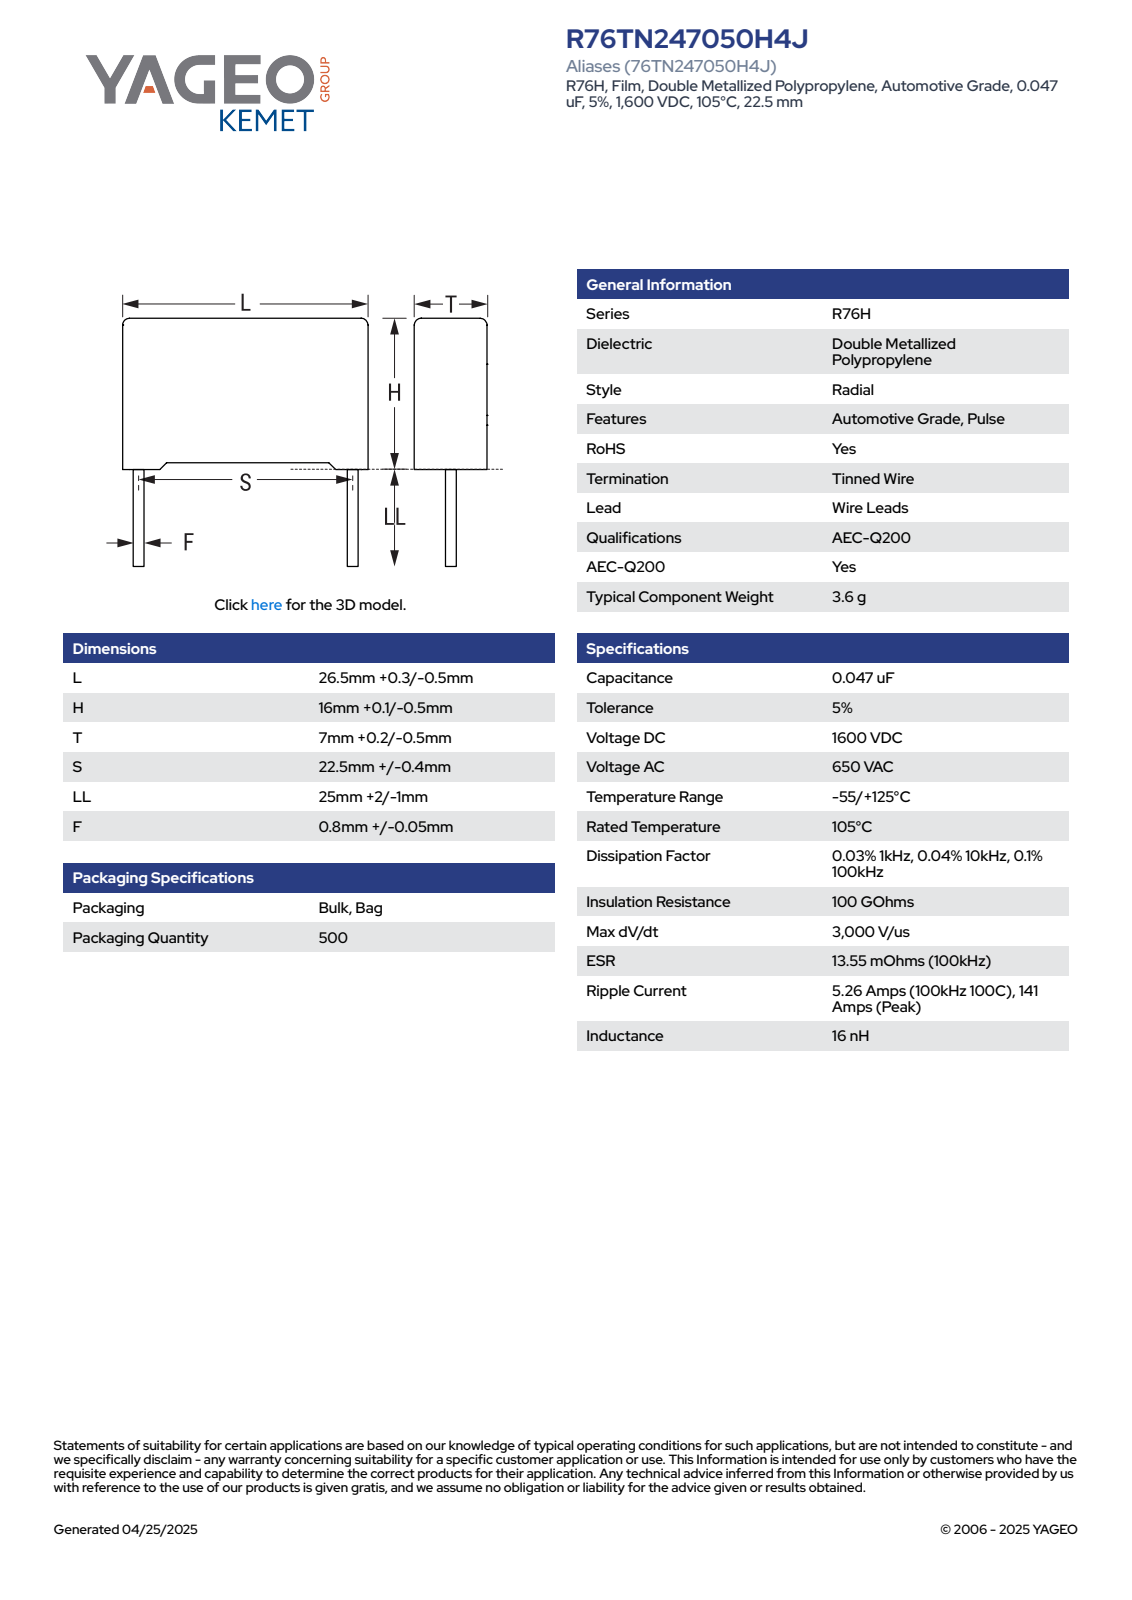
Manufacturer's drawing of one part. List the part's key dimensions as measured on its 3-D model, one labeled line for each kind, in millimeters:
Part name (STEP PRODUCT): CFR_RB2R76_26.5X16X7_L26.8H16.1T7.2S22.5LL27F0.85
STEP written by: SolidWorks 2014 (AUTOMOTIVE_DESIGN)
Units: millimetres
Bodies: 4 solids, 85 faces (77 planar, 8 cylindrical, 0 other)
Overall size (bounding box): 43.1 × 26.8 × 7.21
Volume: 3 015 mm³ · Surface area: 1 673 mm²
Round bosses / shafts (diameter × count): ⌀0.85 ×2
Partial cylindrical surfaces — rounded edges, fillets, slot ends (radius × count): R0.5 ×4
Main face-to-face distances: 7.2, 15.35, 26.8, 15.54, 0.89, 0.56, 0.75, 16.1, 6.31, 5.42
